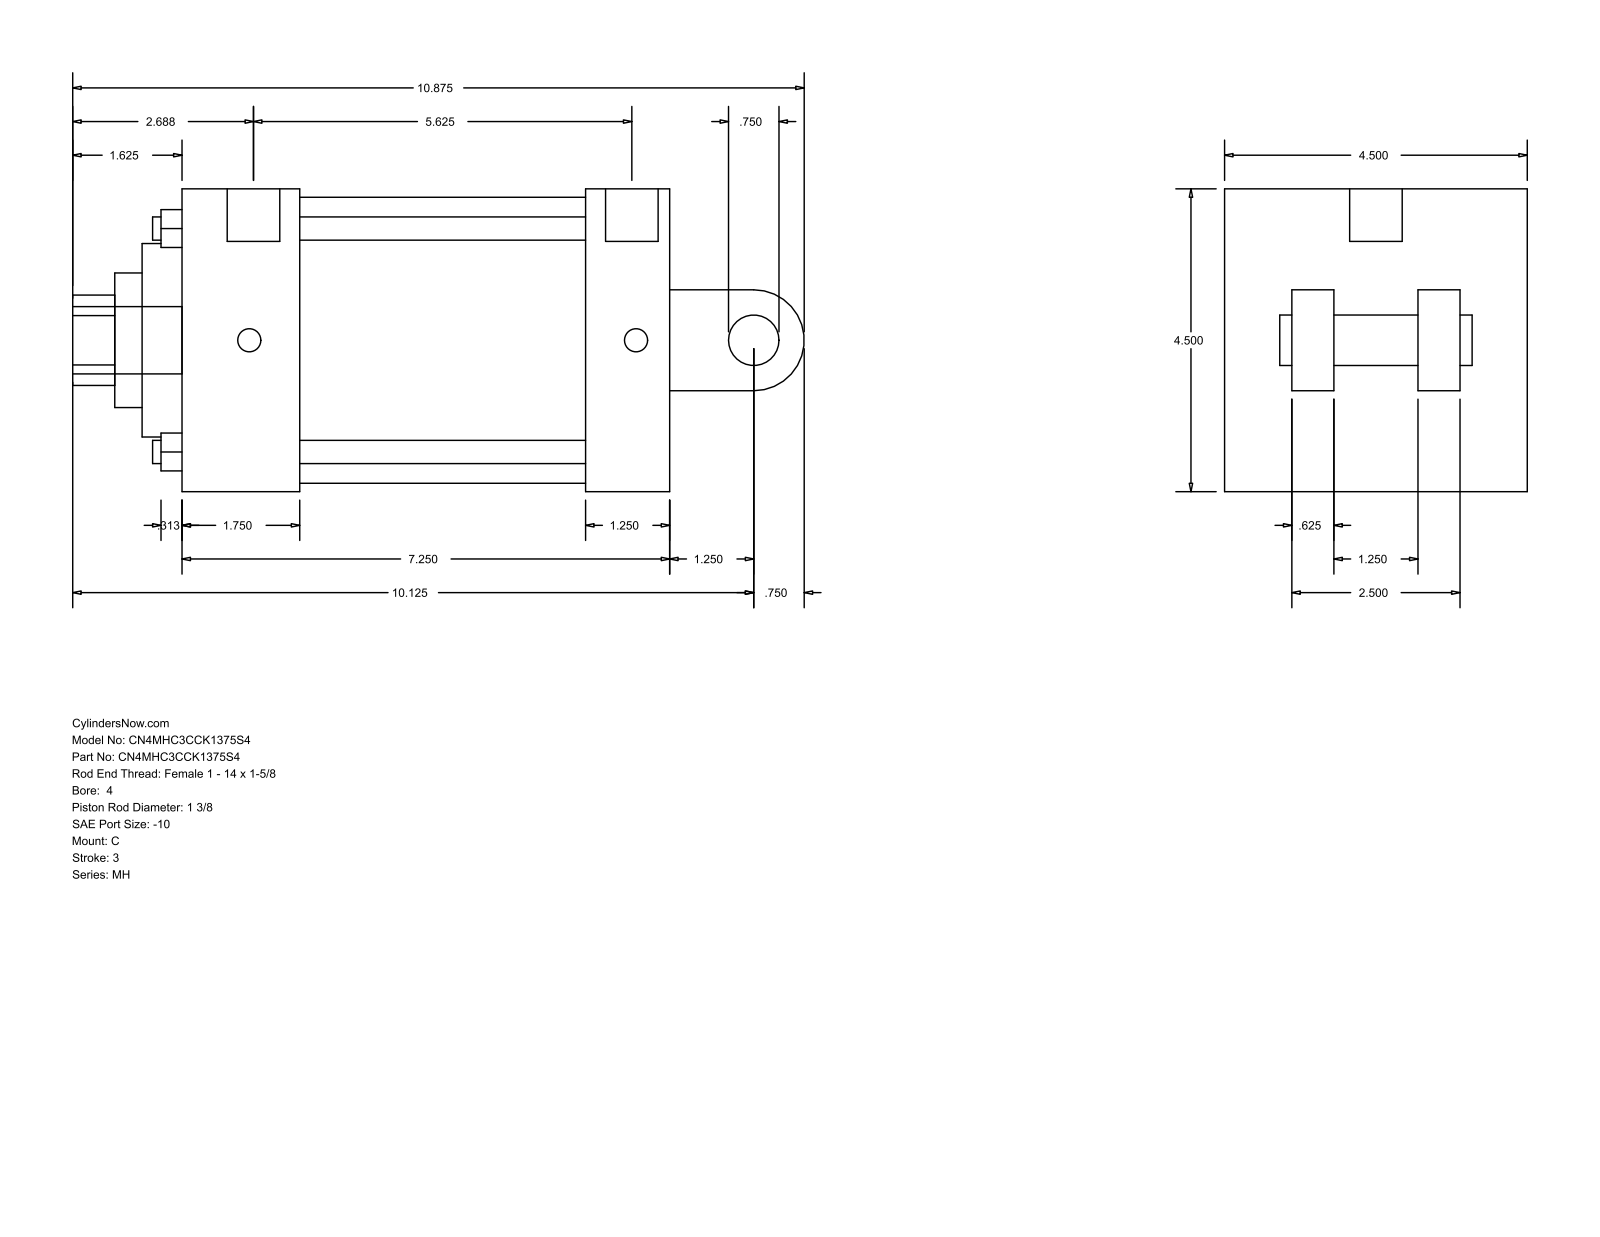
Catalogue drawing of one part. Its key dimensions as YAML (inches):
part_name: "MH_C__0400_1.375"
step_written_by: "GSSL Pune (CONFIG_CONTROL_DESIGN)"
units: inches
bodies: {solids: 0, faces: 101, planar: 71, cylindrical: 30, other: 0}
overall_size: [10.875, 4.5, 4.5]
round_holes:
  - {diameter: 0.345, count: 4}
  - {diameter: 0.344, count: 2}
  - {diameter: 0.781, count: 1}
  - {diameter: 1.375, count: 1}
  - {diameter: 2, count: 1}
  - {diameter: 2.875, count: 1}
  - {diameter: 4.25, count: 1}
round_bosses_or_shafts:
  - {diameter: 0.344, count: 2}
  - {diameter: 1, count: 1}
  - {diameter: 0.781, count: 1}
  - {diameter: 0.75, count: 1}
partial_cylinders:
  - {radius: 0.672, count: 1}
  - {radius: 0.75, count: 1}
face_to_face_distances: [4.5, 7.25, 1.75, 6, 4.25, 5.5, 1.25, 2.875, 1.625, 1.5]
hole_center_spacings: [2.347, 3.32, 4.695, 0.062]
